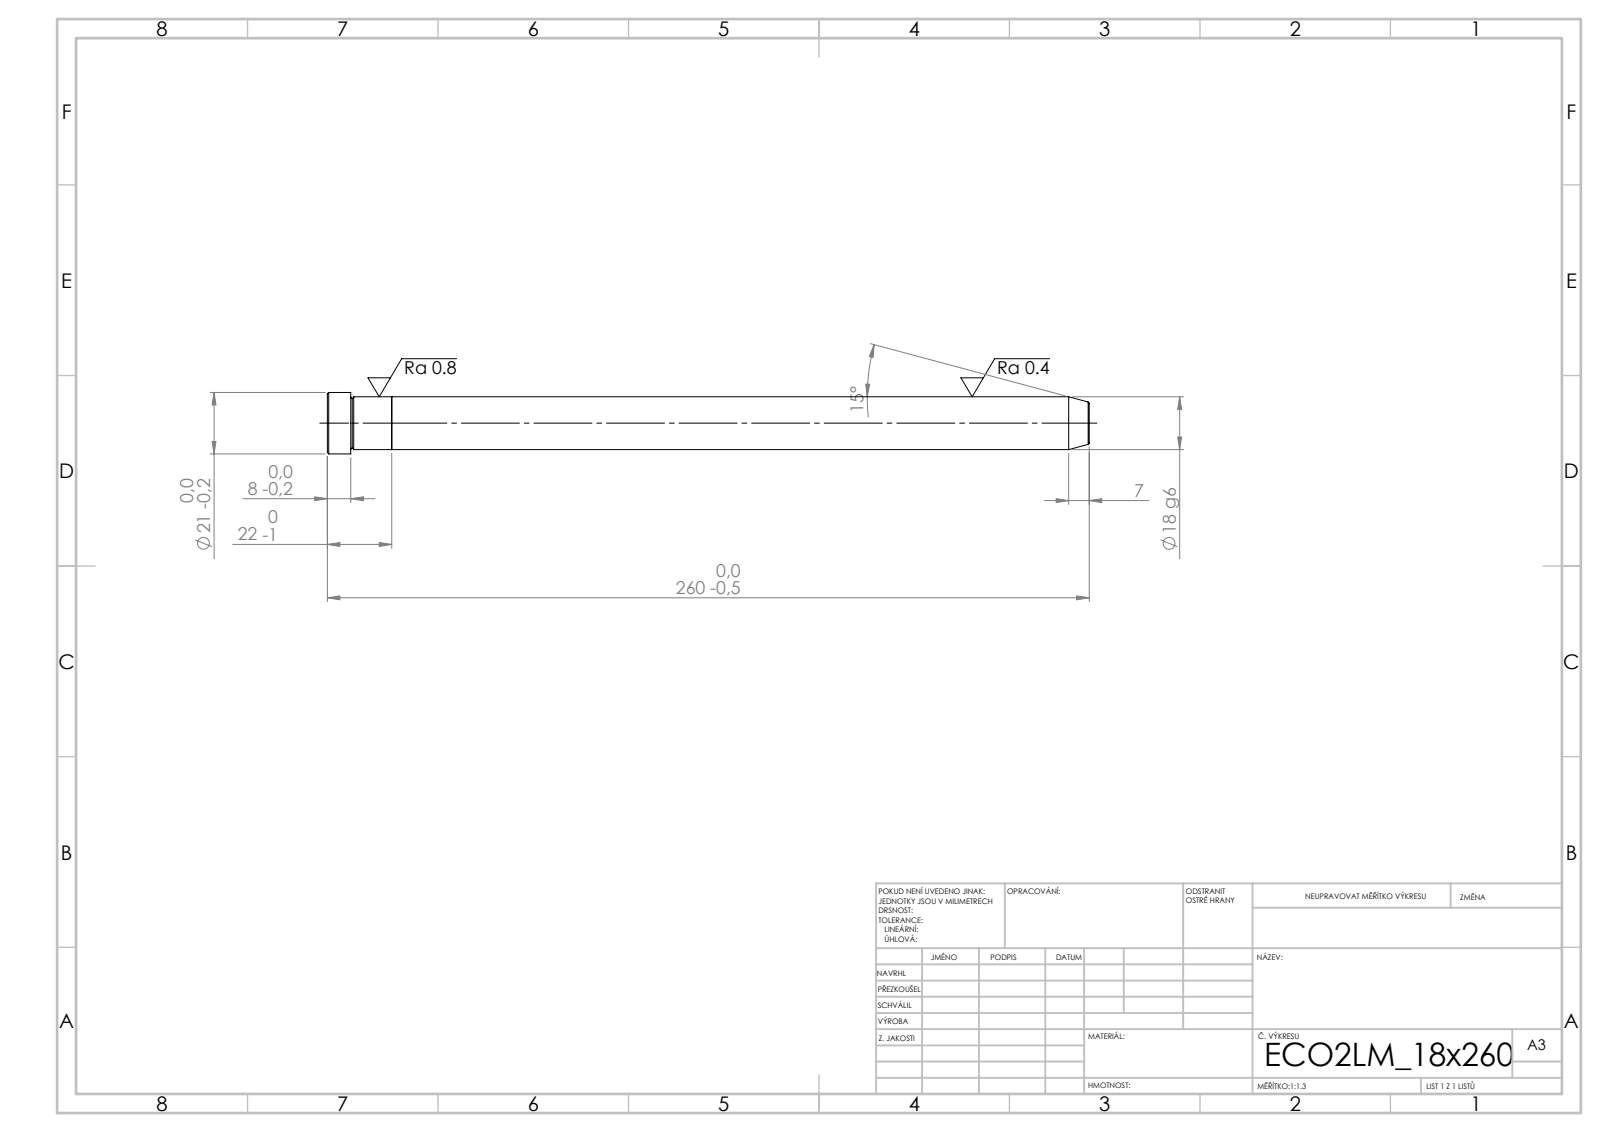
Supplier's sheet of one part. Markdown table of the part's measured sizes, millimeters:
| quantity | value |
| --- | --- |
| STEP written by | SolidWorks 2019 (CONFIG_CONTROL_DESIGN) |
| units | millimeters |
| bodies | 2 solids, 21 faces (5 planar, 6 cylindrical, 10 other) |
| overall size | 260 × 21 × 21 |
| volume | 66 521 mm³ |
| surface area | 15 860 mm² |
| round bosses / shafts (diameter × count) | 21 × 1, 18 × 1 |
| main face-to-face distances | 22, 238, 260, 252, 14, 8 |
